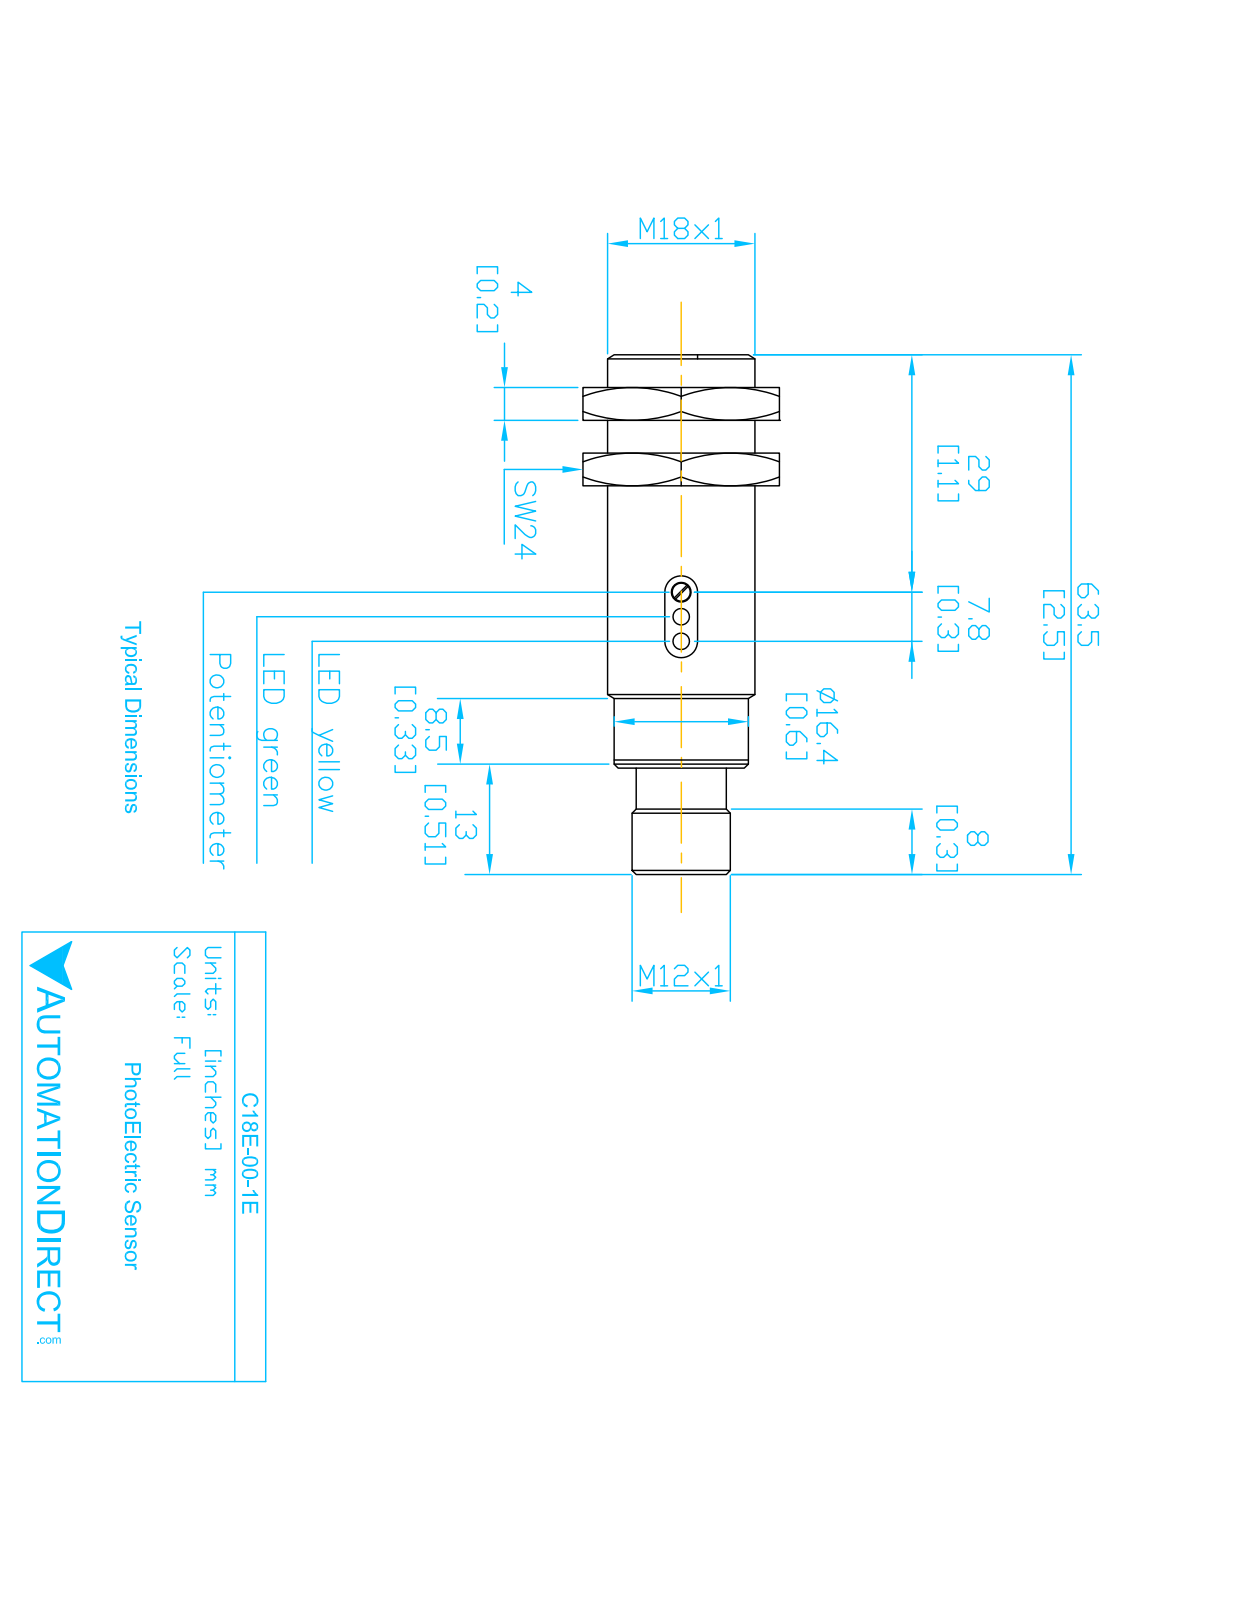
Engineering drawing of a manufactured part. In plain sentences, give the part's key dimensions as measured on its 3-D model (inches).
The part is named "C18E-00-1E". Its 3-D file was written by "SolidWorks 2017 (AUTOMOTIVE_DESIGN)". It is 1 solid with 33 faces: 7 planar, 12 cylindrical and 14 other. Overall it measures 2.5 by 0.709 by 0.709 inches. Its volume is 0.809 cubic inches and its surface area 6.503 square inches. Round holes: 1 of diameter 0.335. Round bosses or shafts: 4 of diameter 0.04, 1 of diameter 0.709, 1 of diameter 0.646, 1 of diameter 0.459, 1 of diameter 0.415. Partial cylindrical surfaces (rounded edges, fillets, slot ends): 2 of radius 0.02. The main face-to-face distances are 2.157, 2.008, 0.15, 2.5, 0.492, 0.343, 2.185, 0.177, 0.028, 0.315.
